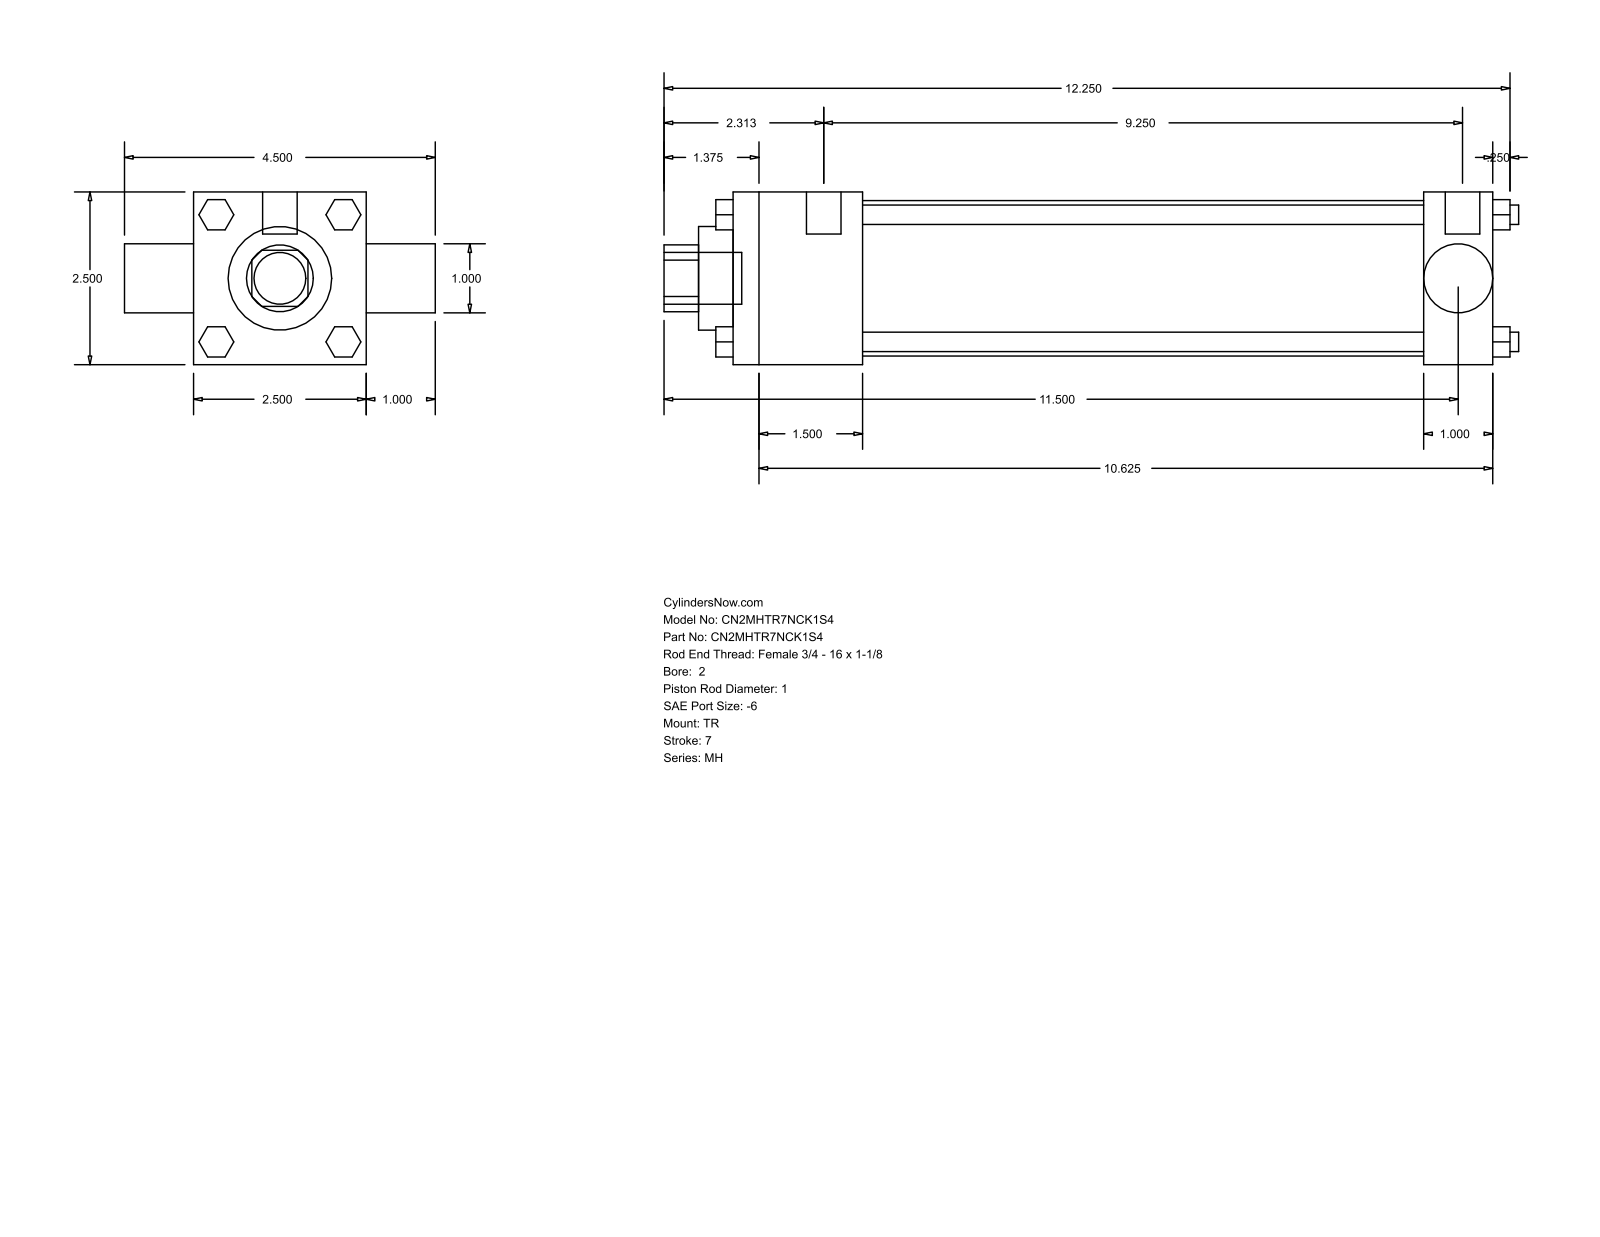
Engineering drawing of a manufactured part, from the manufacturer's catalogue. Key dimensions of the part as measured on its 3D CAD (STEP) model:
Part name (STEP PRODUCT): MH_TR__0200_1
STEP written by: GSSL Pune (CONFIG_CONTROL_DESIGN)
Units: millimetres
Bodies: 0 solids, 120 faces (92 planar, 28 cylindrical, 0 other)
Overall size (bounding box): 314.32 × 114.3 × 63.5
Round holes (diameter × count): ⌀25.35 ×1, ⌀25.4 ×1, ⌀38.1 ×1, ⌀57.15 ×1
Round bosses / shafts (diameter × count): ⌀7.14 ×4, ⌀5.56 ×3, ⌀12.7 ×2, ⌀19.05 ×1
Partial cylindrical surfaces — rounded edges, fillets, slot ends (radius × count): R12.29 ×1
Main face-to-face distances: 63.5, 279.4, 25.4, 47.63, 254, 206.37, 231.77, 88.9, 292.1, 6.35
